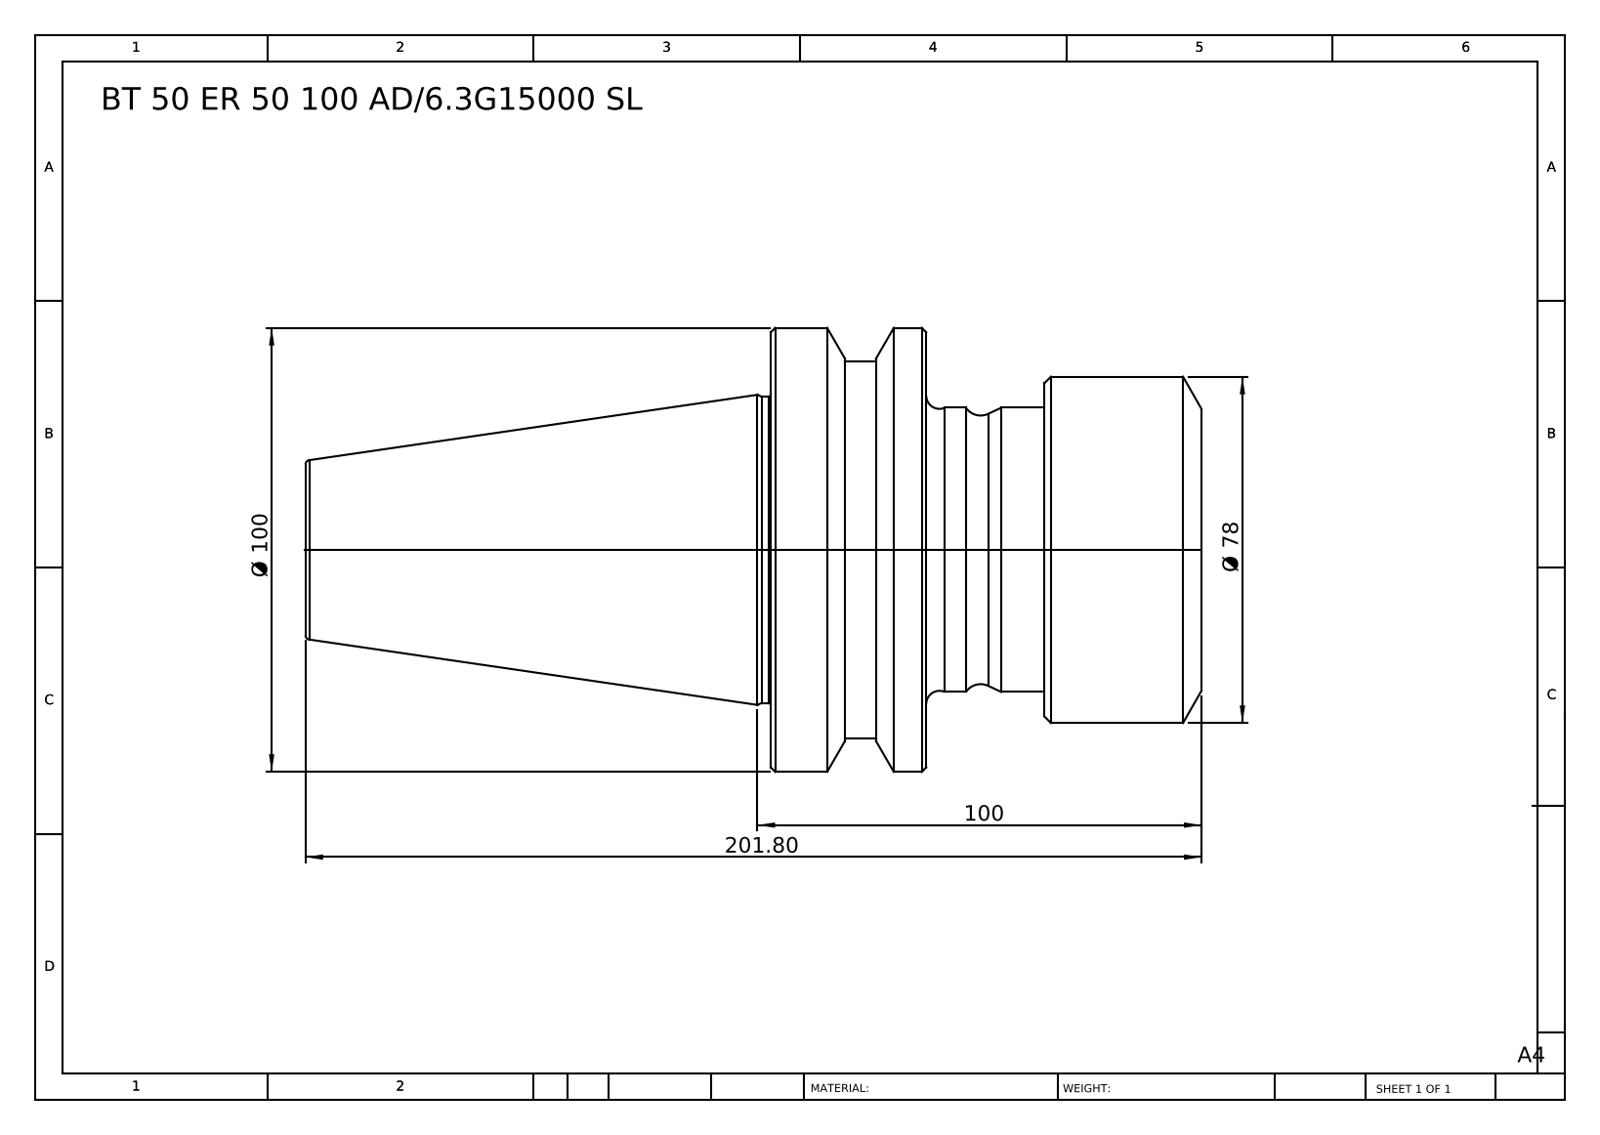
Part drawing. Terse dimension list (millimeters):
name: BT 50 ER 50 100 AD-6.3G15000 SL
written by: SolidWorks 2014 (CONFIG_CONTROL_DESIGN)
unit: mm
bodies: 1 solid, 51 faces (7 planar, 14 cylindrical, 30 other)
size: 201.8 × 100 × 100
volume: 759 480 mm³; area: 60 449 mm²
bosses: 1× ⌀100, 1× ⌀85, 1× ⌀78, 1× ⌀69, 1× ⌀64
face distances: 35, 62, 97, 35.4, 26.6, 61.6, 201.8, 166.4, 139.8, 104.8
